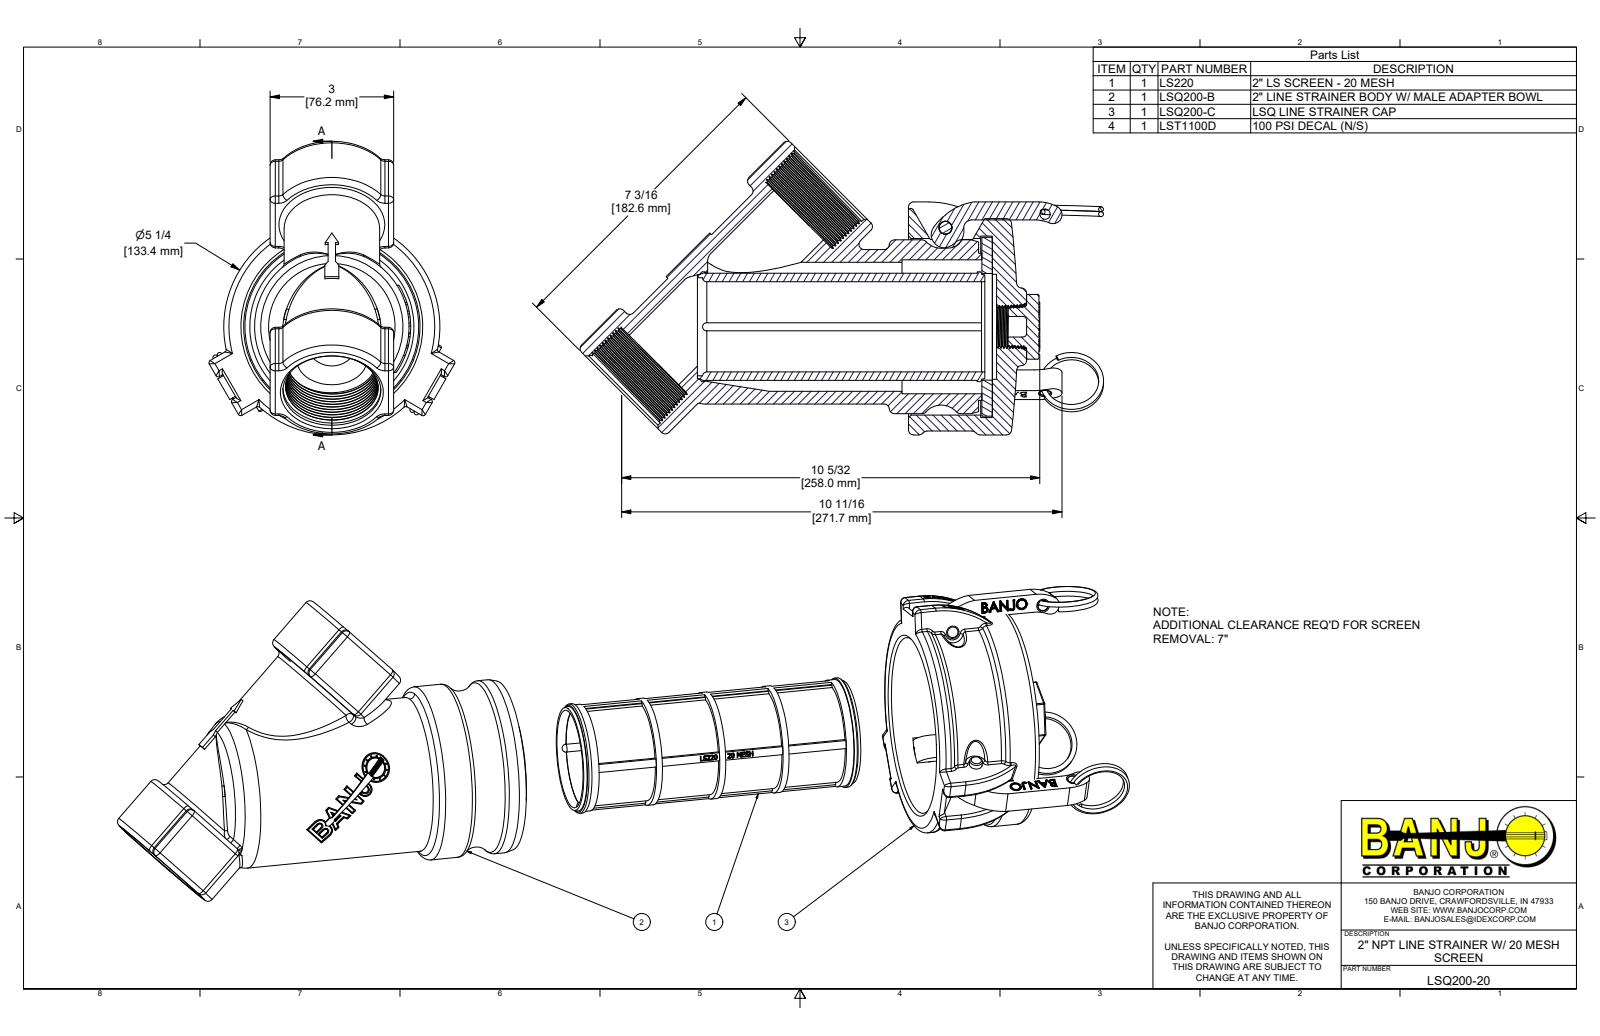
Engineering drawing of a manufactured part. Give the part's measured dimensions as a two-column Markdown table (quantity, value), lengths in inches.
| quantity | value |
| --- | --- |
| part name | LSQ200-20; LSQ200-B; LSQ200-C; LSQ200-MYC (+8 more) |
| STEP written by | Autodesk Inventor 2019 (AUTOMOTIVE_DESIGN) |
| units | inches |
| bodies | 15 solids, 3442 faces (1188 planar, 828 cylindrical, 1426 other) |
| overall size | 19.064 × 7.127 × 5.974 |
| volume | 75.45 in³ |
| surface area | 636.1 in² |
| round holes (diameter × count) | 0.25 × 3, 0.312 × 3, 0.319 × 3, 1.7 × 2, 0.454 × 1, 0.5 × 1, 0.641 × 1, 2.19 × 1, 2.35 × 1, 2.55 × 1, 2.59 × 1, 3.13 × 1 |
| round bosses / shafts (diameter × count) | 0.325 × 3, 0.311 × 3, 5.25 × 1, 4.34 × 1, 4.22 × 1, 3.75 × 1, 3.57 × 1, 2.666 × 1 |
| partial cylindrical surfaces (radius × count) | 0.006 × 353, 0.005 × 51, 0.125 × 47, 0.06 × 27, 0.03 × 18, 0.929 × 6, 0.25 × 5, 0.1 × 4 |
| main face-to-face distances | 0.25, 0.255, 2.04, 2.035, 1.785, 0.45, 0.61, 0.1, 0.355, 0.03 |
| hole center spacings | 2.442, 3.359, 5.685 |
